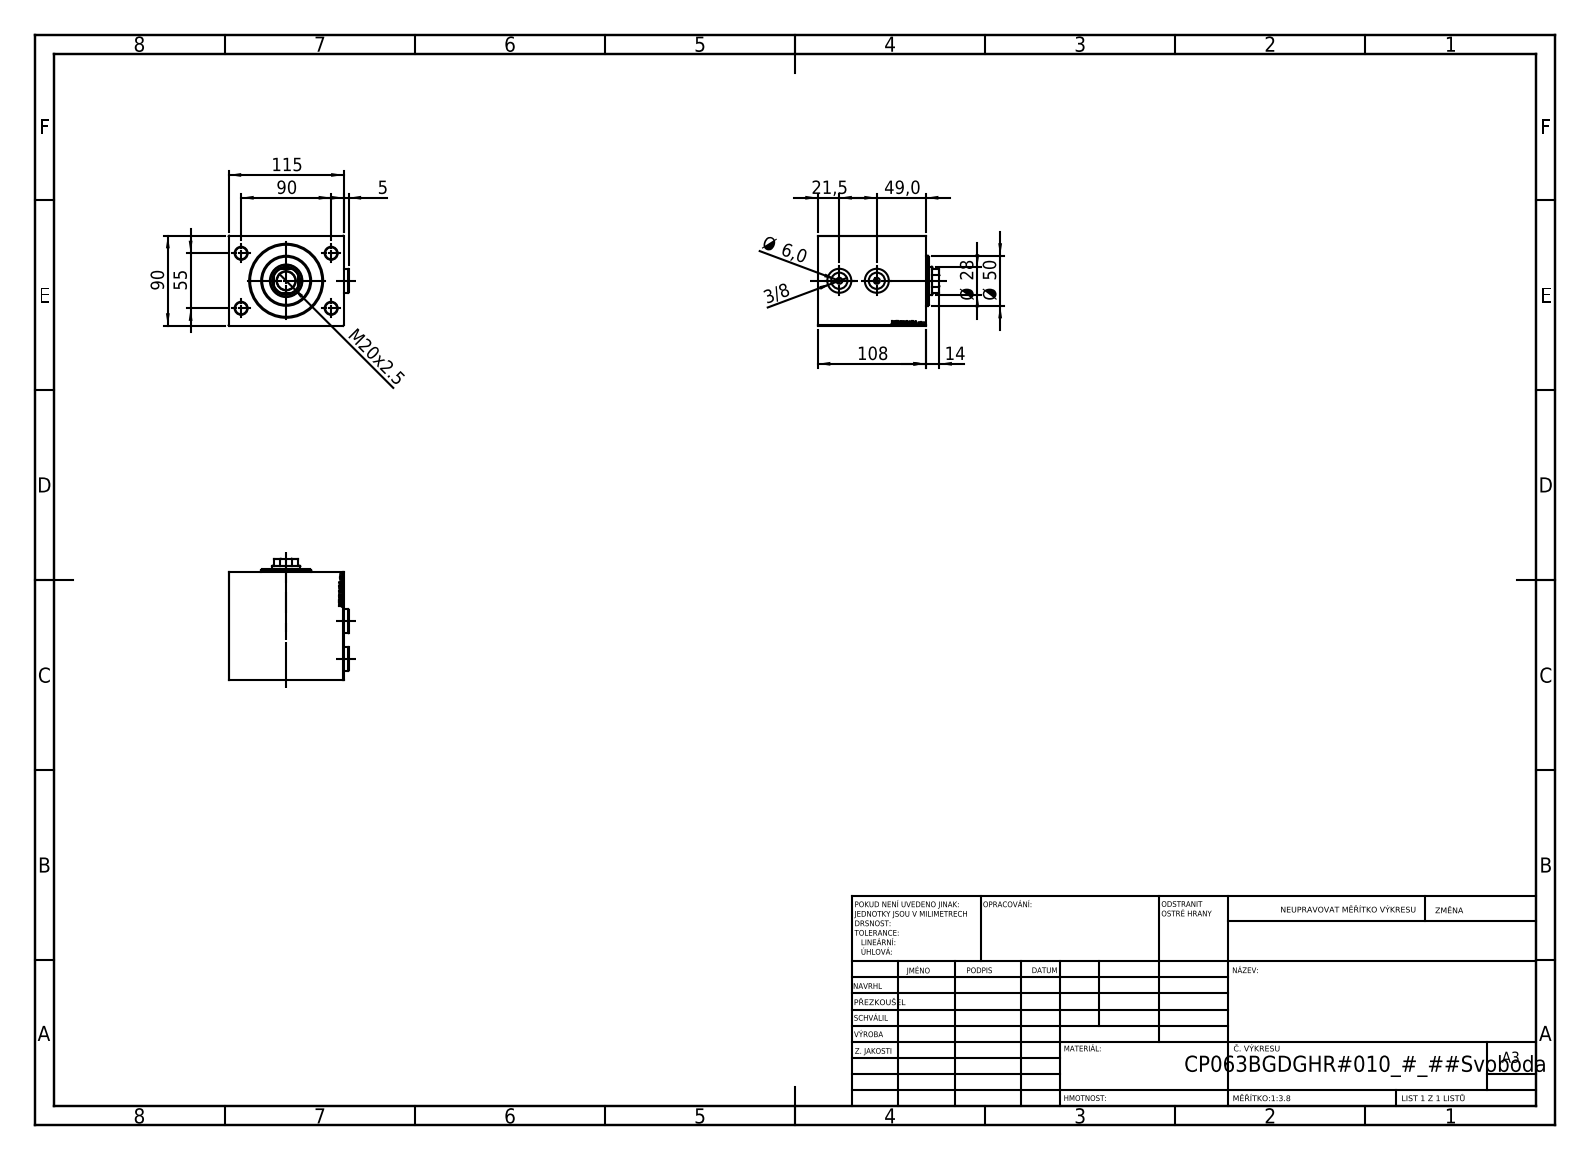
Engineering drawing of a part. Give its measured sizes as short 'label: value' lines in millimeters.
name: V450CP_B; V450CP_B_VCP; PLUG; V450CP_VC_B
written by: SolidWorks 2019 (CONFIG_CONTROL_DESIGN)
unit: mm
bodies: 5 solids, 959 faces (441 planar, 84 cylindrical, 434 other)
size: 121.5 × 119.9 × 90
volume: 1 068 000 mm³; area: 138 485 mm²
holes: 4× ⌀12, 2× ⌀4, 2× ⌀6, 2× ⌀9.73, 2× ⌀15, 2× ⌀16.17, 2× ⌀24, 1× ⌀18.5, 1× ⌀28, 1× ⌀31.5, 1× ⌀32.5, 1× ⌀63
bosses: 1× ⌀50
rounds: 1× R13.5
face distances: 90, 115, 108, 17.5, 90.5, 57.5, 40, 50.5, 47.5, 10
hole spacings: 52.74, 55, 90, 105.48, 37.5, 42.22
